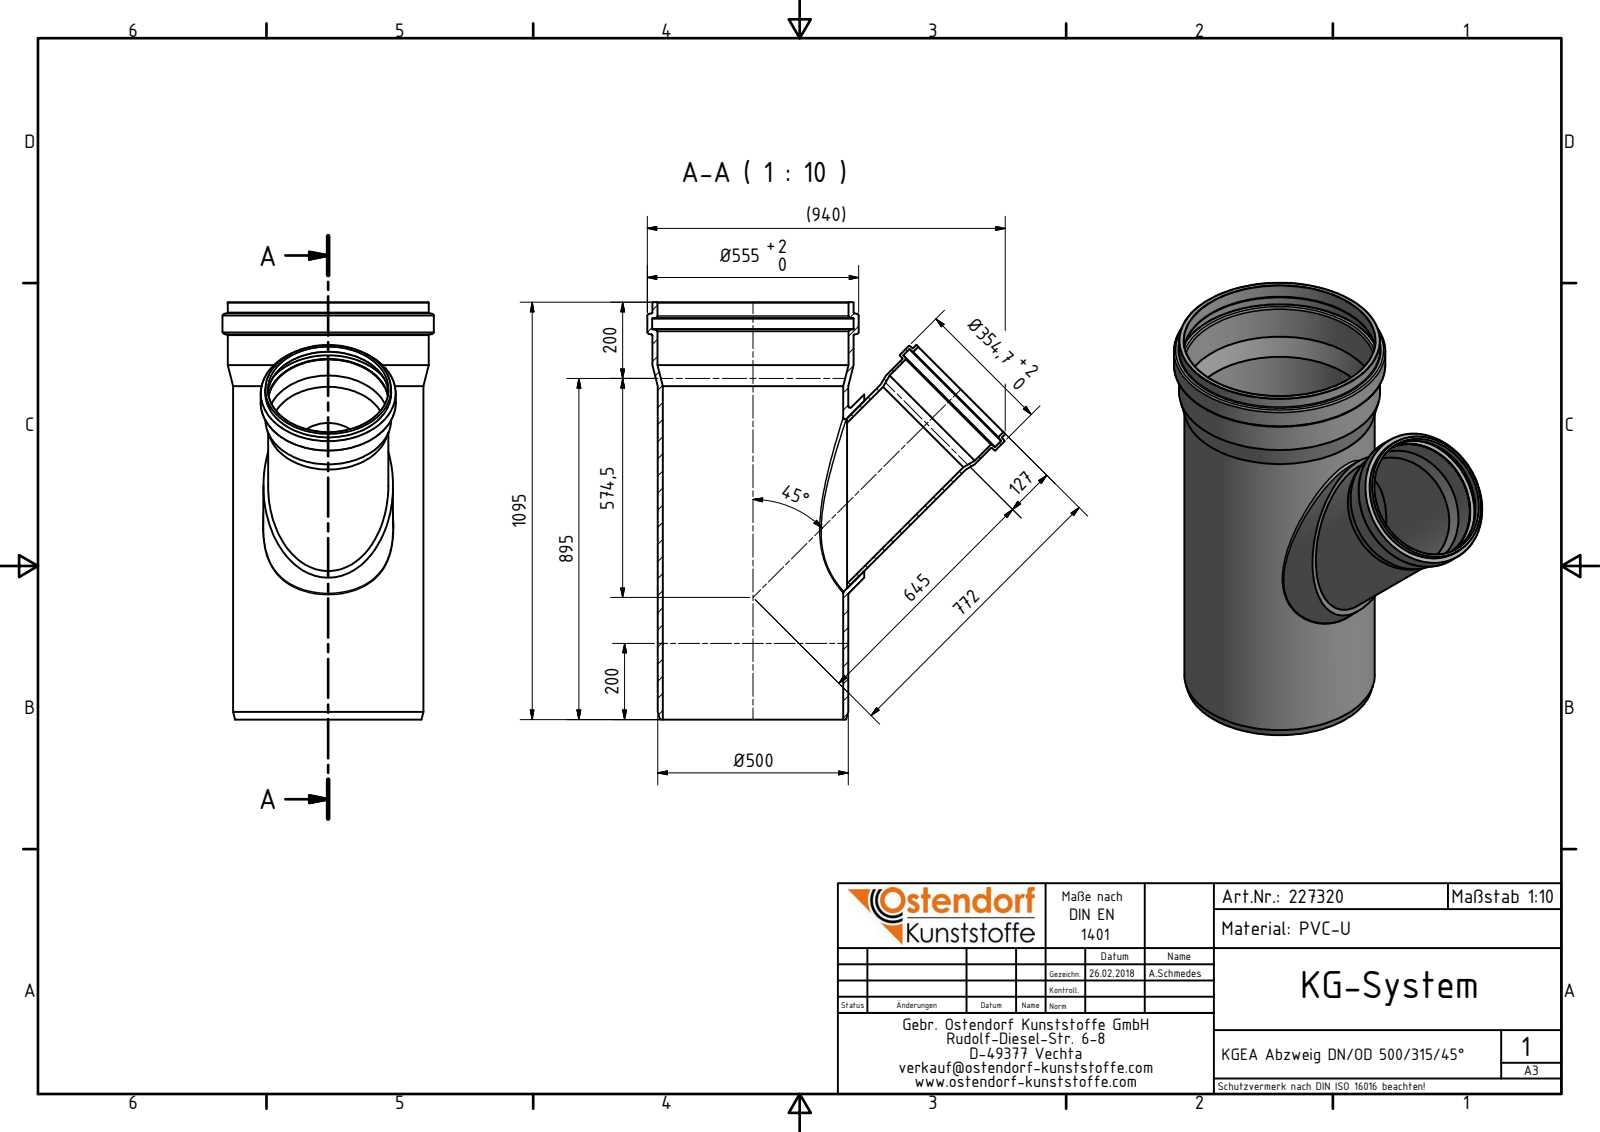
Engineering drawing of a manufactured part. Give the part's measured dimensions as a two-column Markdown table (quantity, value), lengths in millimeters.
| quantity | value |
| --- | --- |
| part name | 227320 KGEA Abzweig DN_OD 500_315_45°; 227320 KGEA Abzweig DN_OD 500_315_45° Abzweig |
| STEP written by | Autodesk Inventor 2016 (AUTOMOTIVE_DESIGN) |
| units | millimeters |
| bodies | 2 solids, 60 faces (6 planar, 19 cylindrical, 35 other) |
| overall size | 1095 × 940 × 555 |
| volume | 25 810 000 mm³ |
| surface area | 4 378 000 mm² |
| round holes (diameter × count) | 316.3 × 2, 298.2 × 1, 315.6 × 1, 316 × 1, 340.9 × 1, 474 × 1, 502 × 1, 529 × 1 |
| round bosses / shafts (diameter × count) | 555 × 1, 528 × 1, 500 × 1, 354.7 × 1, 340.2 × 1, 330.1 × 1, 329.8 × 1, 315.6 × 1 |
| main face-to-face distances | 45.32, 1095, 46.55 |
